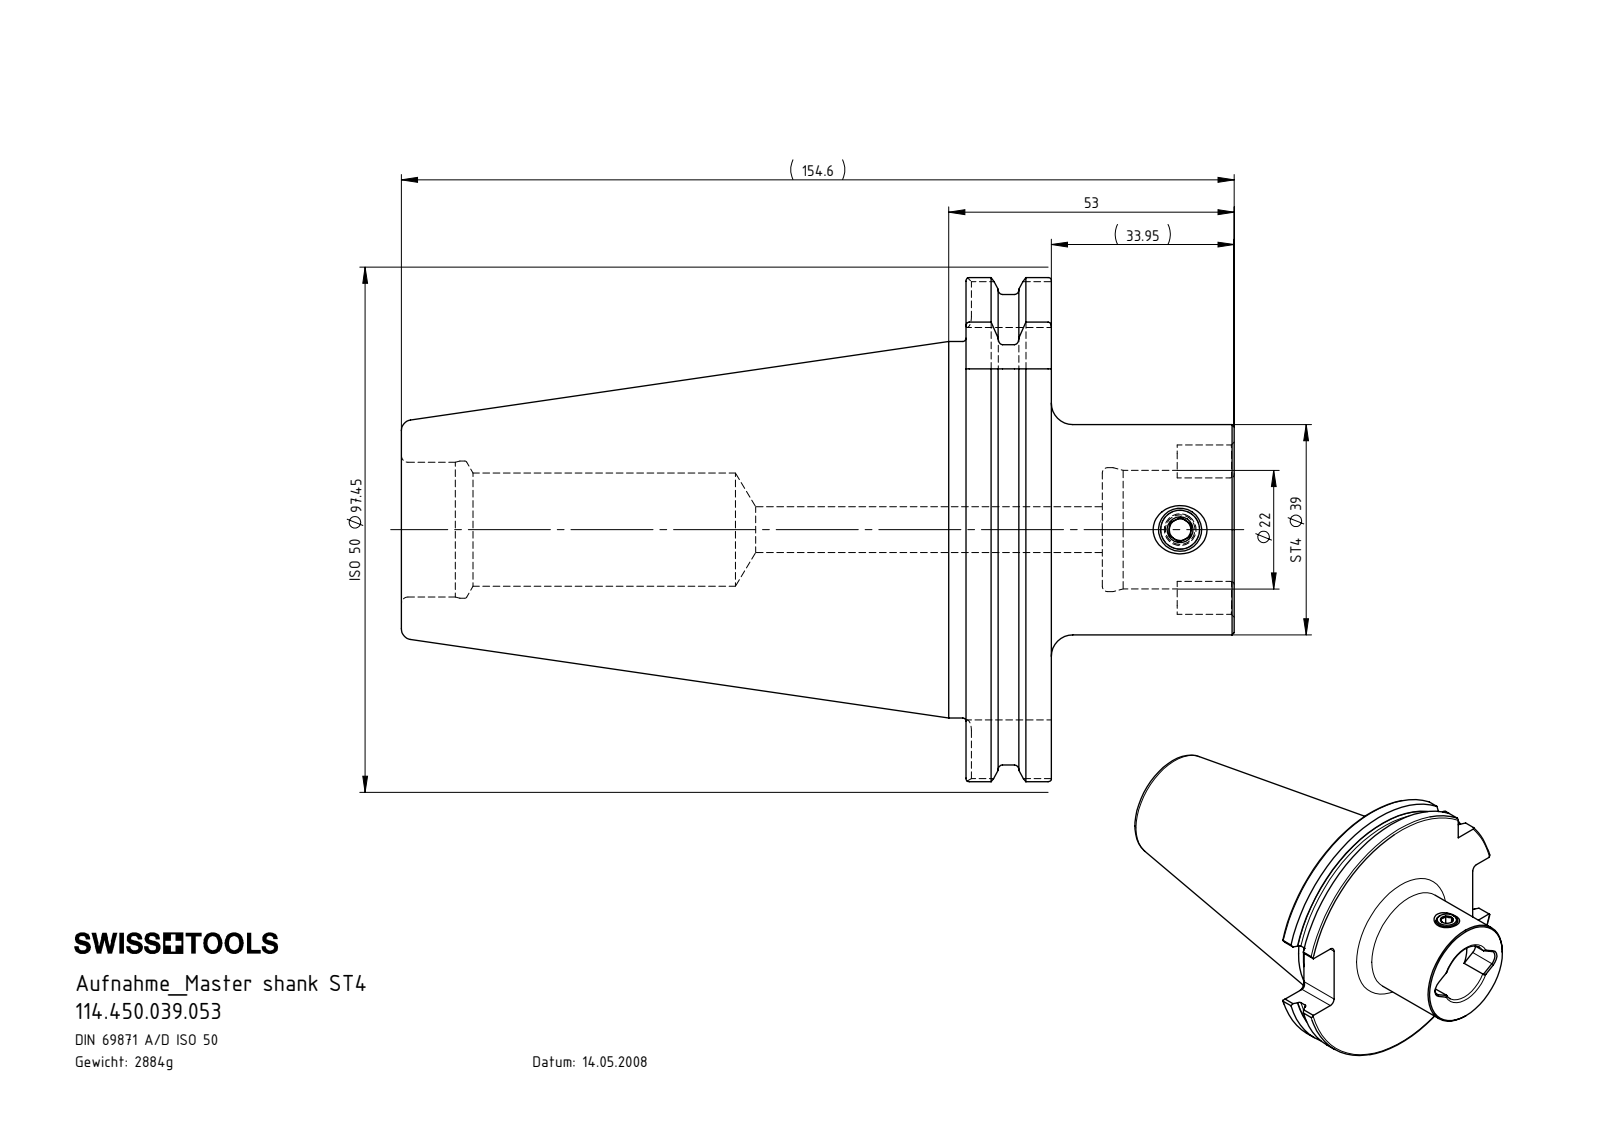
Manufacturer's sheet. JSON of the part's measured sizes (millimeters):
{"part_name": "ST4-ER1.001.011_A; SK5-ST4.K01.053_B; SK5.ST4.K01.053", "step_written_by": "SolidWorks 2017 (AUTOMOTIVE_DESIGN)", "units": "millimeters", "bodies": {"solids": 2, "faces": 126, "planar": 54, "cylindrical": 30, "other": 42}, "overall_size": [154.6, 97.45, 93.51], "volume_mm3": 367379, "surface_area_mm2": 47548, "round_holes": [[4, 1], [7.25, 1], [8.5, 1], [21, 1], [22, 1], [23, 1], [25, 1], [25.45, 1]], "round_bosses_or_shafts": [[91, 1], [69.85, 1], [39, 1], [8, 1]], "partial_cylinders_radius": [[2, 8], [3.2, 2], [48.73, 1]], "face_to_face_distances": [15.85, 49.8, 33.95, 104.8, 120.65, 154.6, 72.8, 130.1, 25.3, 9.45]}
